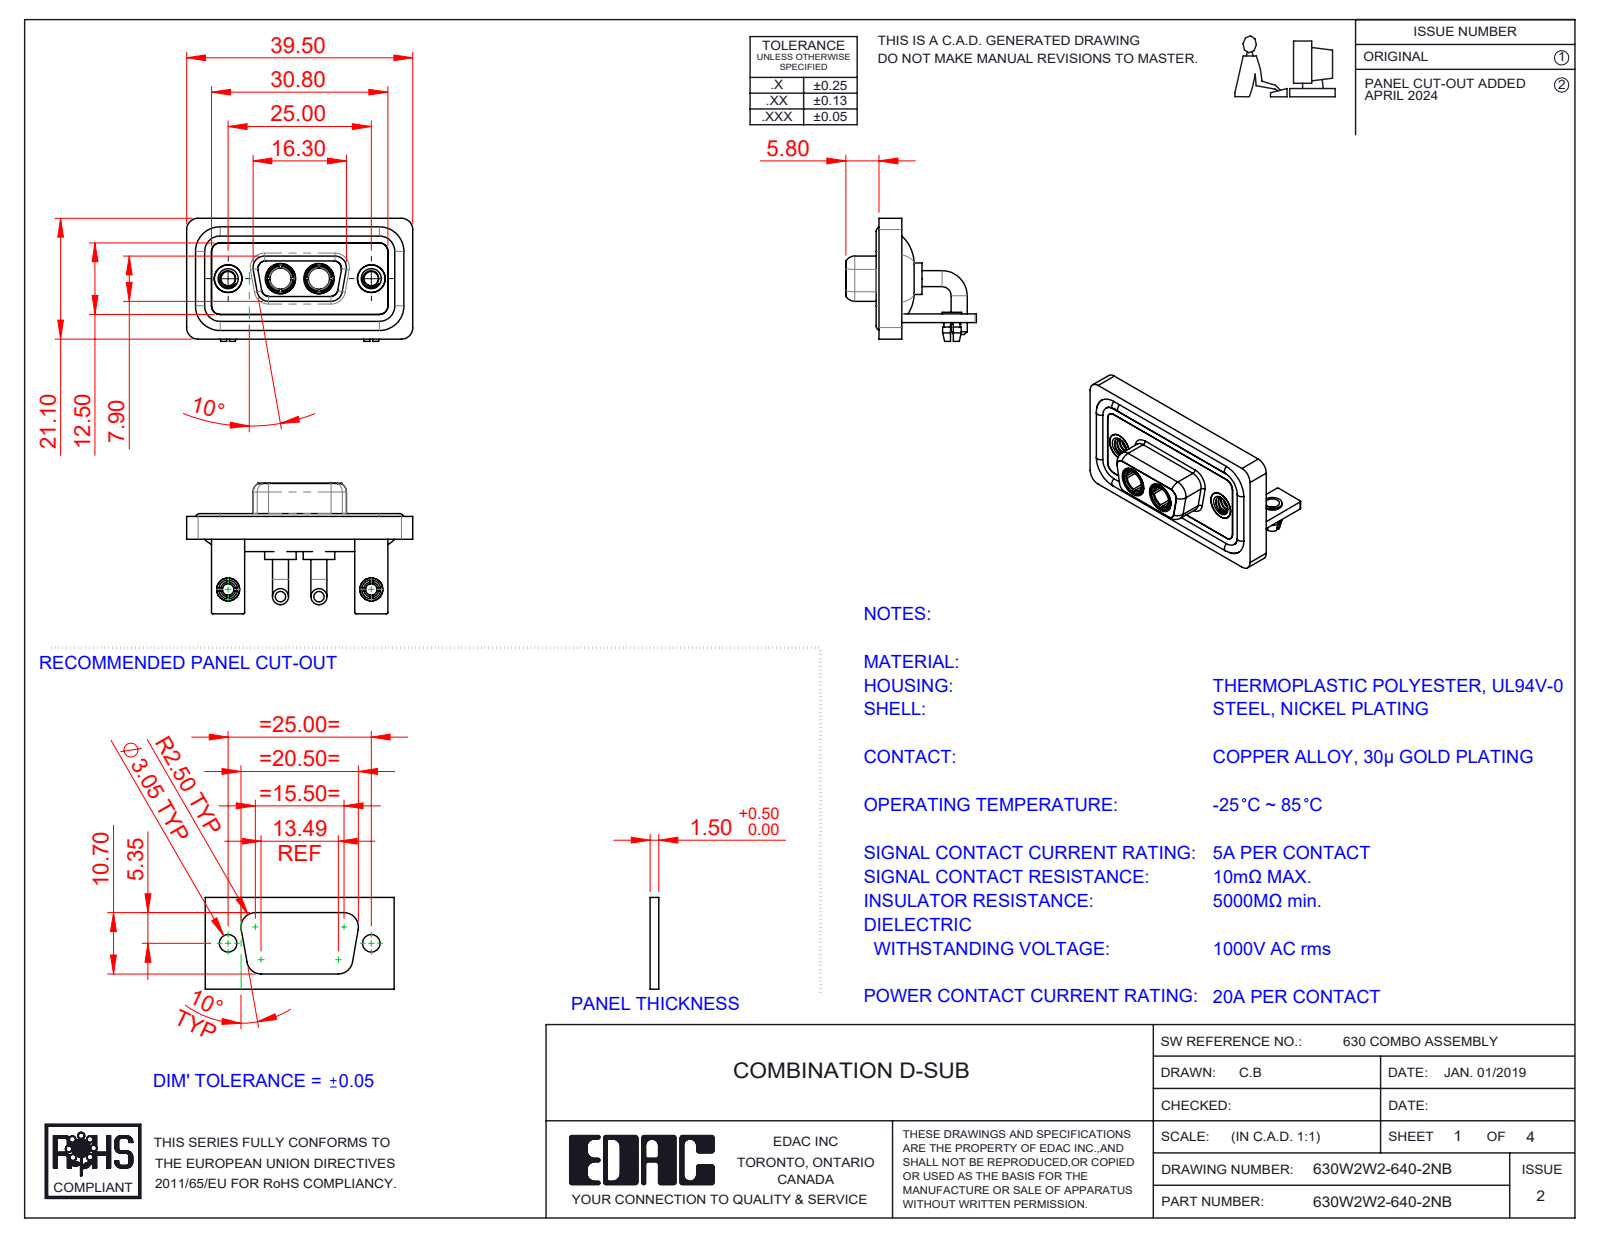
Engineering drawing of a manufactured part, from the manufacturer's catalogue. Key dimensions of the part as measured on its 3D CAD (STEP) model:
Part name (STEP PRODUCT): 630Combo Threaded Rivet_A; 630Combo Housing_2W2; 630W2W2-640-2NB; 630Combo Stabilizer Bracket_50 Contacts (+5 more)
STEP written by: SolidWorks 2023 (CONFIG_CONTROL_DESIGN)
Units: millimetres
Bodies: 15 solids, 676 faces (231 planar, 292 cylindrical, 153 other)
Overall size (bounding box): 39.5 × 22.8 × 21.5
Volume: 5 211 mm³ · Surface area: 8 735 mm²
Round holes (diameter × count): ⌀2.5 ×4, ⌀4.85 ×4, ⌀2 ×2, ⌀3.2 ×2, ⌀3.7 ×2, ⌀4 ×2, ⌀4.05 ×2, ⌀5 ×2, ⌀5.3 ×2
Round bosses / shafts (diameter × count): ⌀2.8 ×4, ⌀1.6 ×4, ⌀5.5 ×2, ⌀5.2 ×2, ⌀4.96 ×2, ⌀4.95 ×2, ⌀4.8 ×2, ⌀4.75 ×2
Partial cylindrical surfaces — rounded edges, fillets, slot ends (radius × count): R2 ×19, R1.5 ×18, R0.25 ×16, R1.35 ×8, R1.6 ×8, R0.5 ×5, R0.6 ×4, R0.65 ×4
Main face-to-face distances: 0.4, 2.9, 1.5, 1.8, 1.1, 3.7, 0.8, 2.5, 1.6, 3.1
Hole centre spacings: 9.14, 15.86, 25, 6.72
